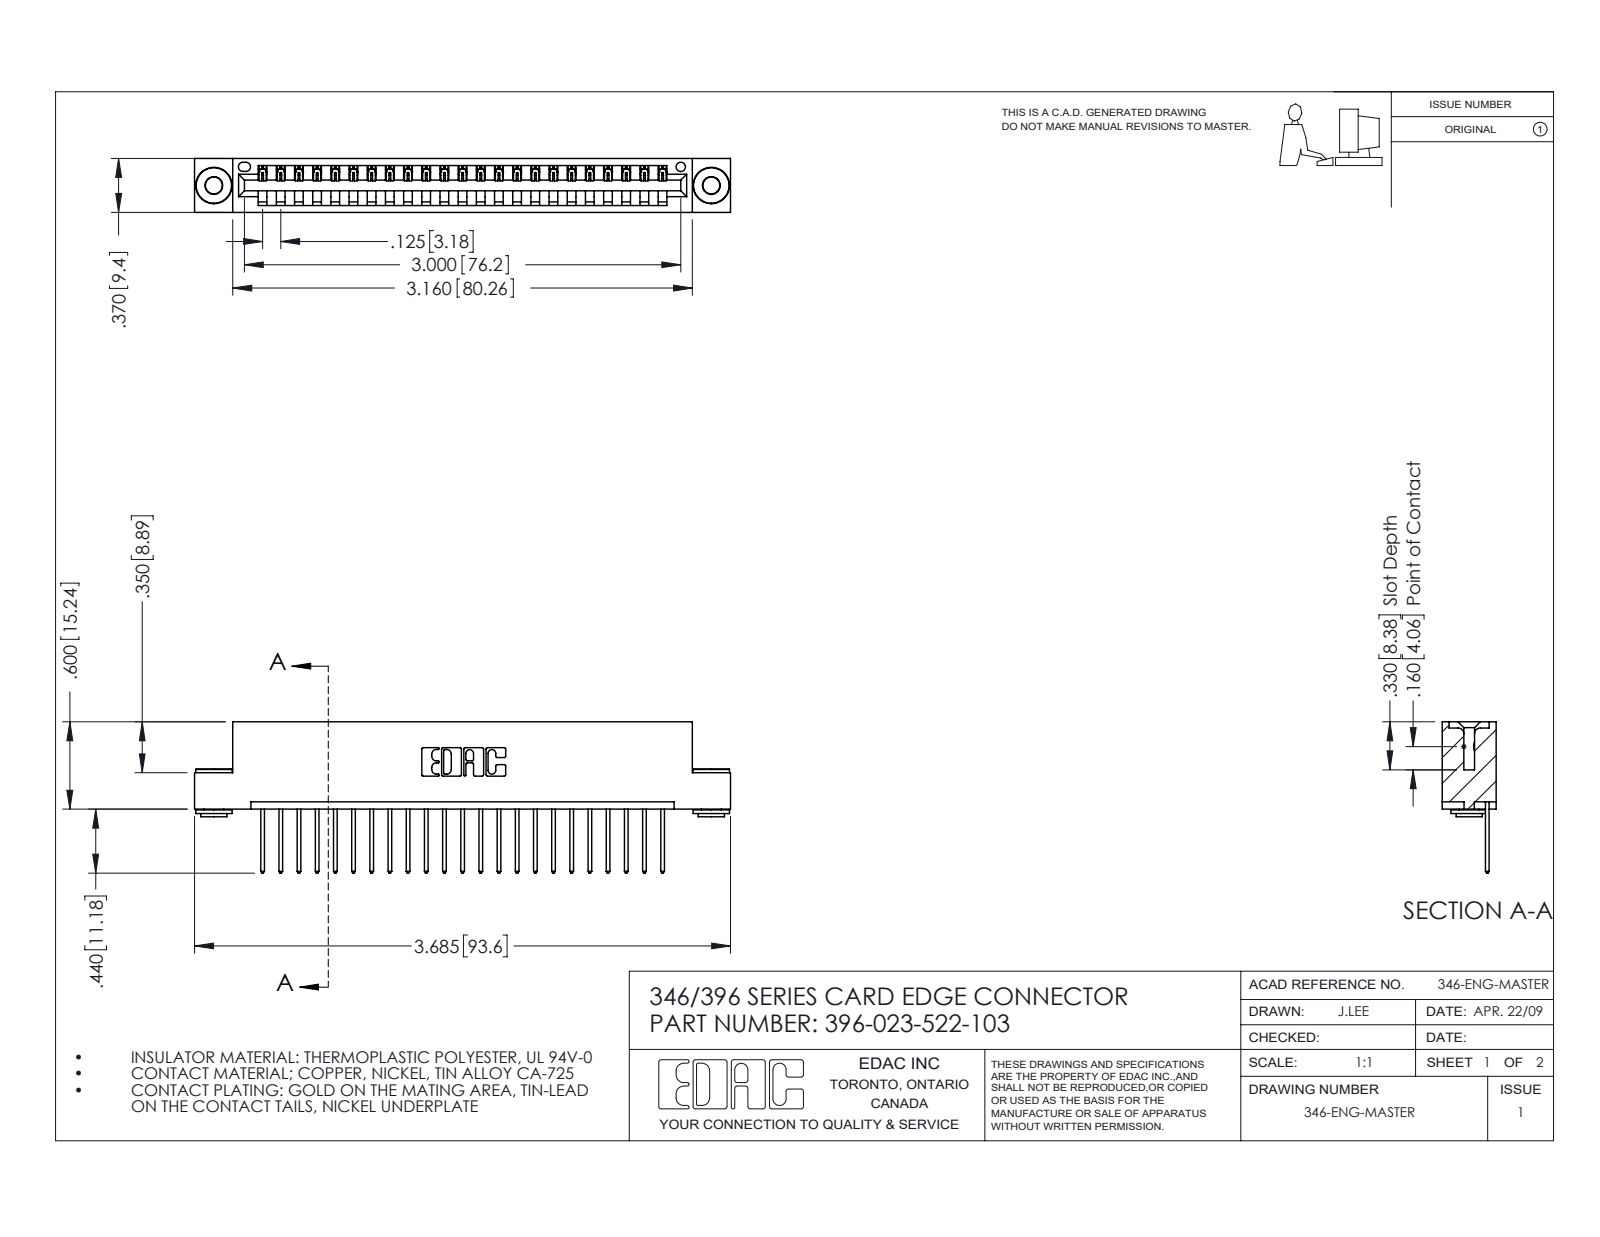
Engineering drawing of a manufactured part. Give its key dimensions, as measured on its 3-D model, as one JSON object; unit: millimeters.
{"part_name": "396-023-522-103; 345-292-001_345-293-122; 346 Part_Flush Mounting Lugs - 0.156 Dia-TH; 345-250-002_345-250-002-102", "step_written_by": "SolidWorks 2016 (CONFIG_CONTROL_DESIGN)", "units": "millimeters", "bodies": {"solids": 26, "faces": 1494, "planar": 1006, "cylindrical": 480, "other": 8}, "overall_size": [93.6, 26.4, 9.4], "volume_mm3": 8850, "surface_area_mm2": 11160, "round_holes": [[2.9, 2], [4, 2], [1.6, 1]], "round_bosses_or_shafts": [[6.4, 2], [4.6, 2], [3.5, 2]], "partial_cylinders_radius": [[0.2, 46], [0.3, 46], [0.3, 22], [0.2, 6], [0.8, 6], [0.7, 3], [0.8, 2], [1, 2]], "face_to_face_distances": [1.2, 8.2, 6.4, 9.4, 0.6, 1.8, 7.6, 3.8, 5.6, 2.5], "hole_center_spacings": [6.2, 81.6, 86.9]}
